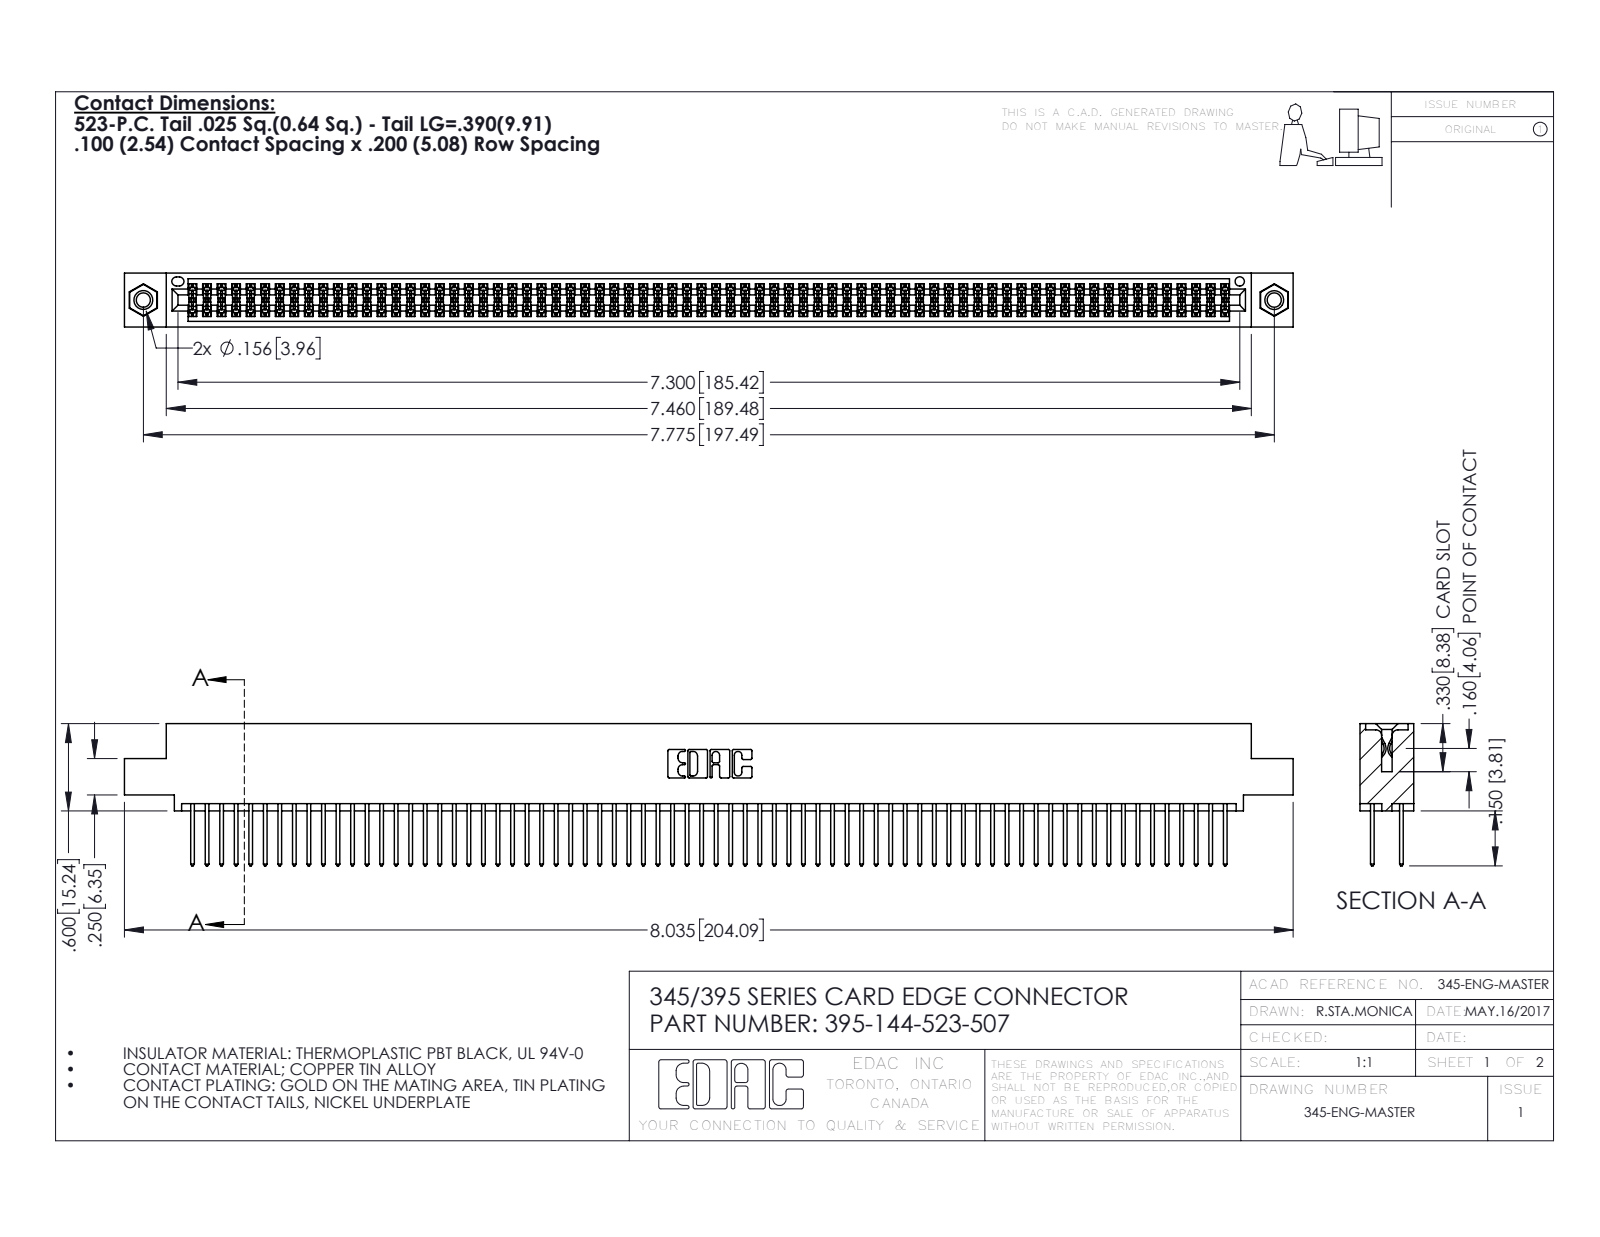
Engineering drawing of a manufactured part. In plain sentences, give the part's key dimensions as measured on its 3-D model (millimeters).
The part is named "345 Part_0.110 Offset - 0.156 Dia-TI; 395-144-523-507; 345-250-001_345-250-005-103; 345-292-001_345-293-123". Its 3-D file was written by "SolidWorks 2016 (CONFIG_CONTROL_DESIGN)". It is 147 solids with 7390 faces: 4868 planar, 2506 cylindrical and 16 other. Overall it measures 204.1 by 24.8 by 9.4 millimeters. Its volume is 20 320 cubic millimeters and its surface area 32 050 square millimeters. Round holes: 2 of diameter 2.5, 2 of diameter 3.2, 2 of diameter 4, 1 of diameter 1.6. Round bosses or shafts: 2 of diameter 3.9. Partial cylindrical surfaces (rounded edges, fillets, slot ends): 216 of radius 0.2, 144 of radius 0.3, 22 of radius 0.3, 6 of radius 0.2, 6 of radius 0.8, 3 of radius 0.7, 2 of radius 0.4, 2 of radius 0.5. The main face-to-face distances are 1.8, 7.6, 5.1, 2.5, 6.9, 0.6, 9.4, 5.7, 4.4, 3.8. The hole center spacings are 6.9, 191.5, 197.5.
